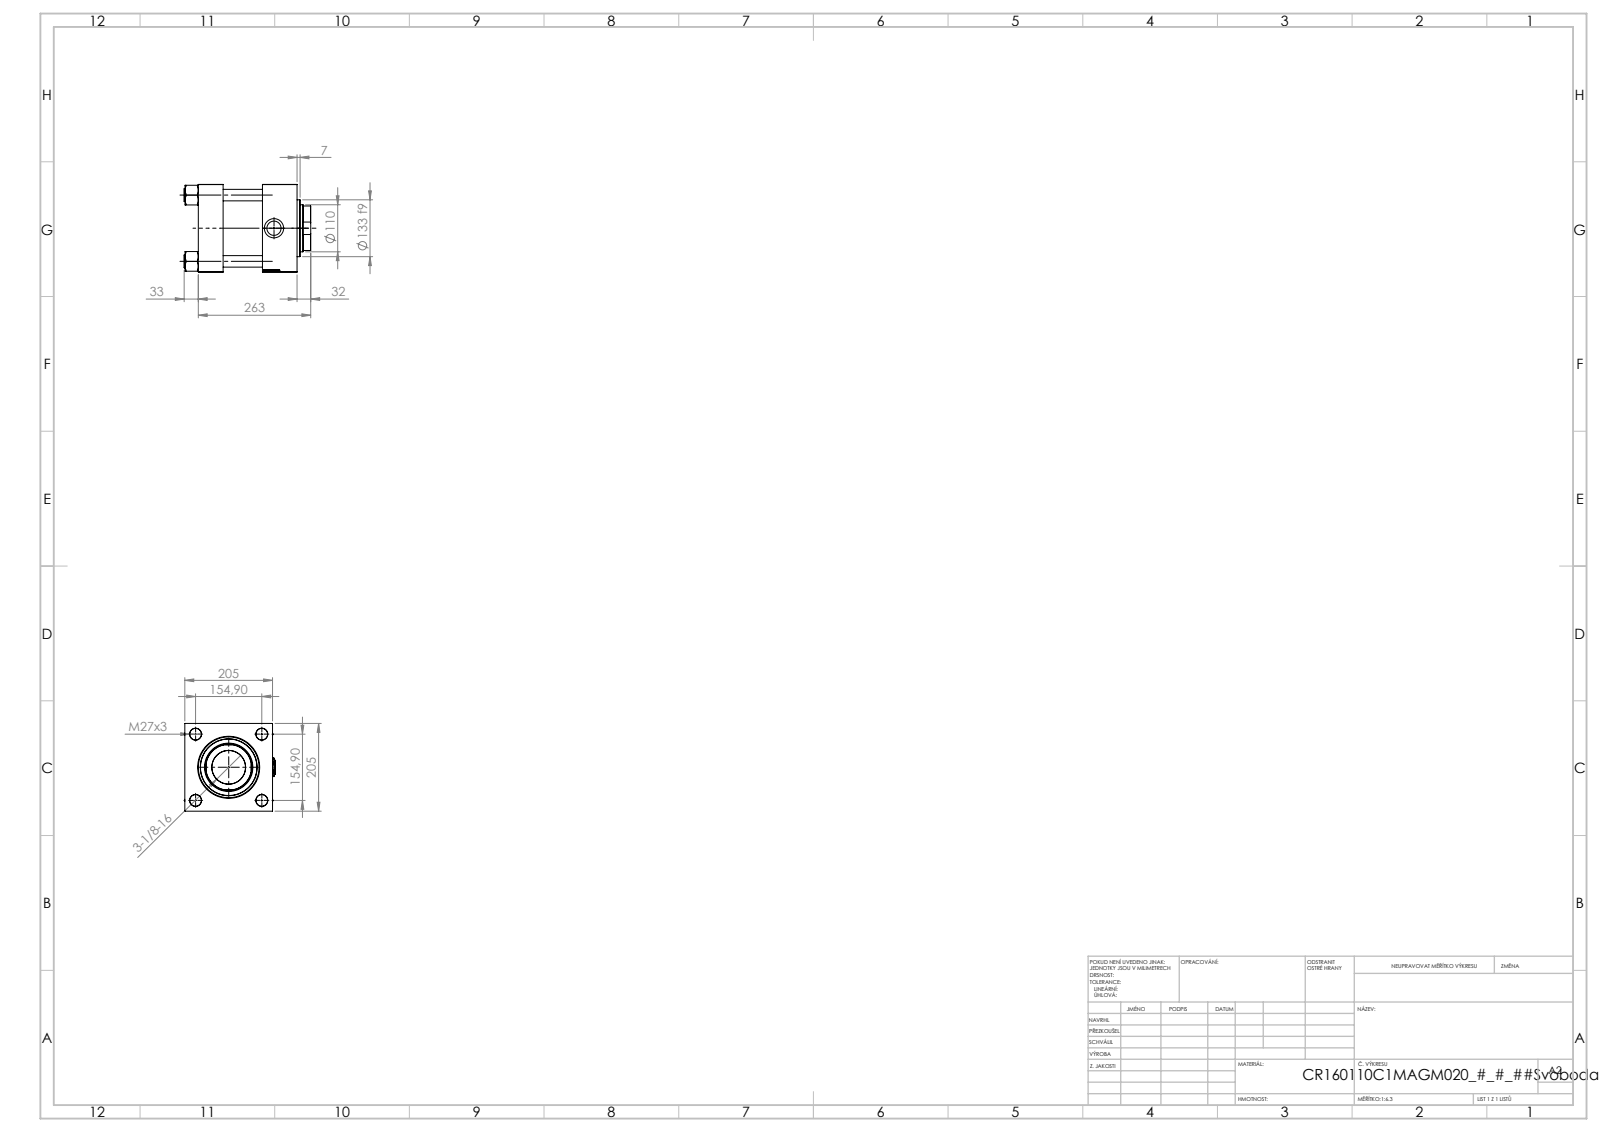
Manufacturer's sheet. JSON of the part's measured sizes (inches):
{"part_name": "V215_VC_A; Zatka_pro_OIL_PORT; NUT_M5_C; V215CR_C_TYCINKA (+2 more)", "step_written_by": "SolidWorks 2019 (CONFIG_CONTROL_DESIGN)", "units": "inches", "bodies": {"solids": 12, "faces": 1244, "planar": 597, "cylindrical": 91, "other": 556}, "overall_size": [11.654, 8.408, 8.071], "volume_in3": 465, "surface_area_in2": 1126, "round_holes": [[1.063, 4], [0.276, 2], [1.309, 2], [1.772, 2], [3.091, 1], [4.331, 1], [4.449, 1], [4.724, 1], [5.591, 1], [6.299, 1]], "round_bosses_or_shafts": [[1.181, 4], [6.535, 1], [5.236, 1]], "partial_cylinders_radius": [[2.126, 1]], "face_to_face_distances": [8.071, 2.283, 3.622, 5.906, 9.094, 6.811, 3.189, 7.965, 5.681, 2.059], "hole_center_spacings": [4.312, 6.098, 8.624]}
